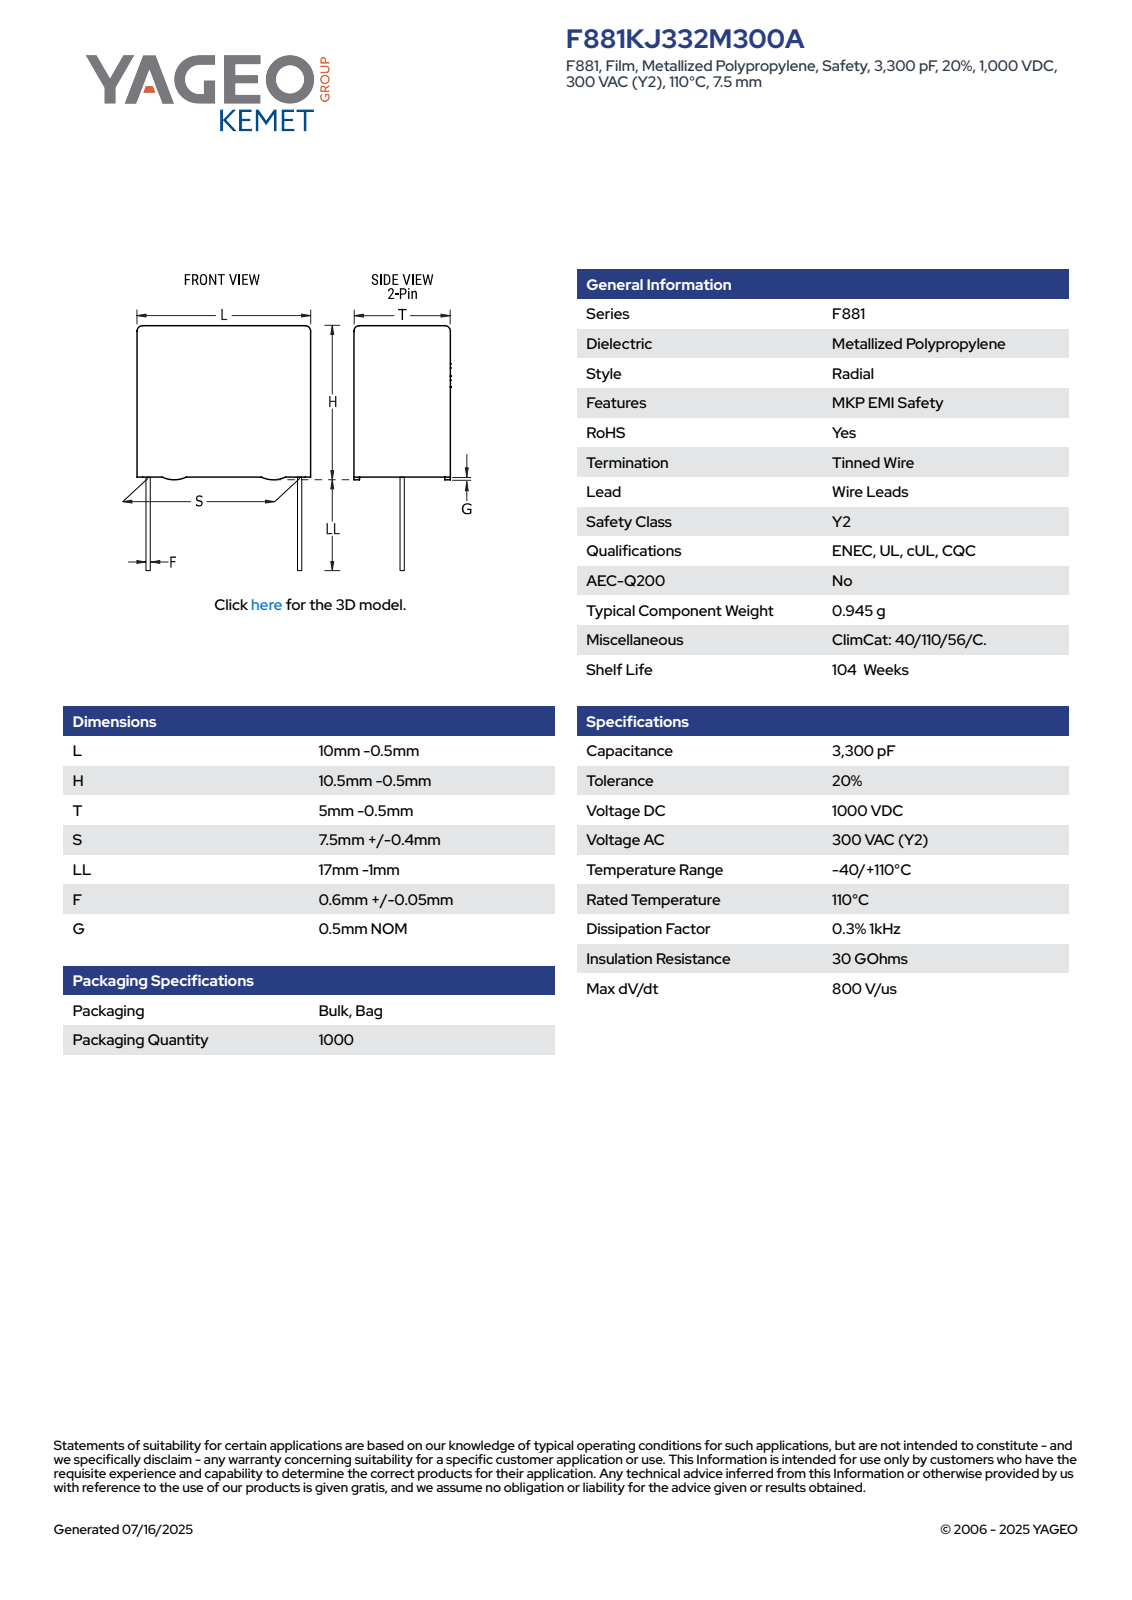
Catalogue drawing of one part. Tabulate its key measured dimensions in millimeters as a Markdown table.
| quantity | value |
| --- | --- |
| part name | CFR_RBG_10X10.5X5_L9.5H10T4.5S7.5LL16F0.65G0.5 |
| STEP written by | SolidWorks 2014 (AUTOMOTIVE_DESIGN) |
| units | millimeters |
| bodies | 4 solids, 89 faces (81 planar, 8 cylindrical, 0 other) |
| overall size | 26 × 9.5 × 4.5 |
| volume | 416 mm³ |
| surface area | 430 mm² |
| round bosses / shafts (diameter × count) | 0.65 × 2 |
| partial cylindrical surfaces (radius × count) | 0.5 × 4 |
| main face-to-face distances | 4.5, 9.5, 4.24, 3.98, 0.5, 10, 16, 16.5, 26, 4.05 |
